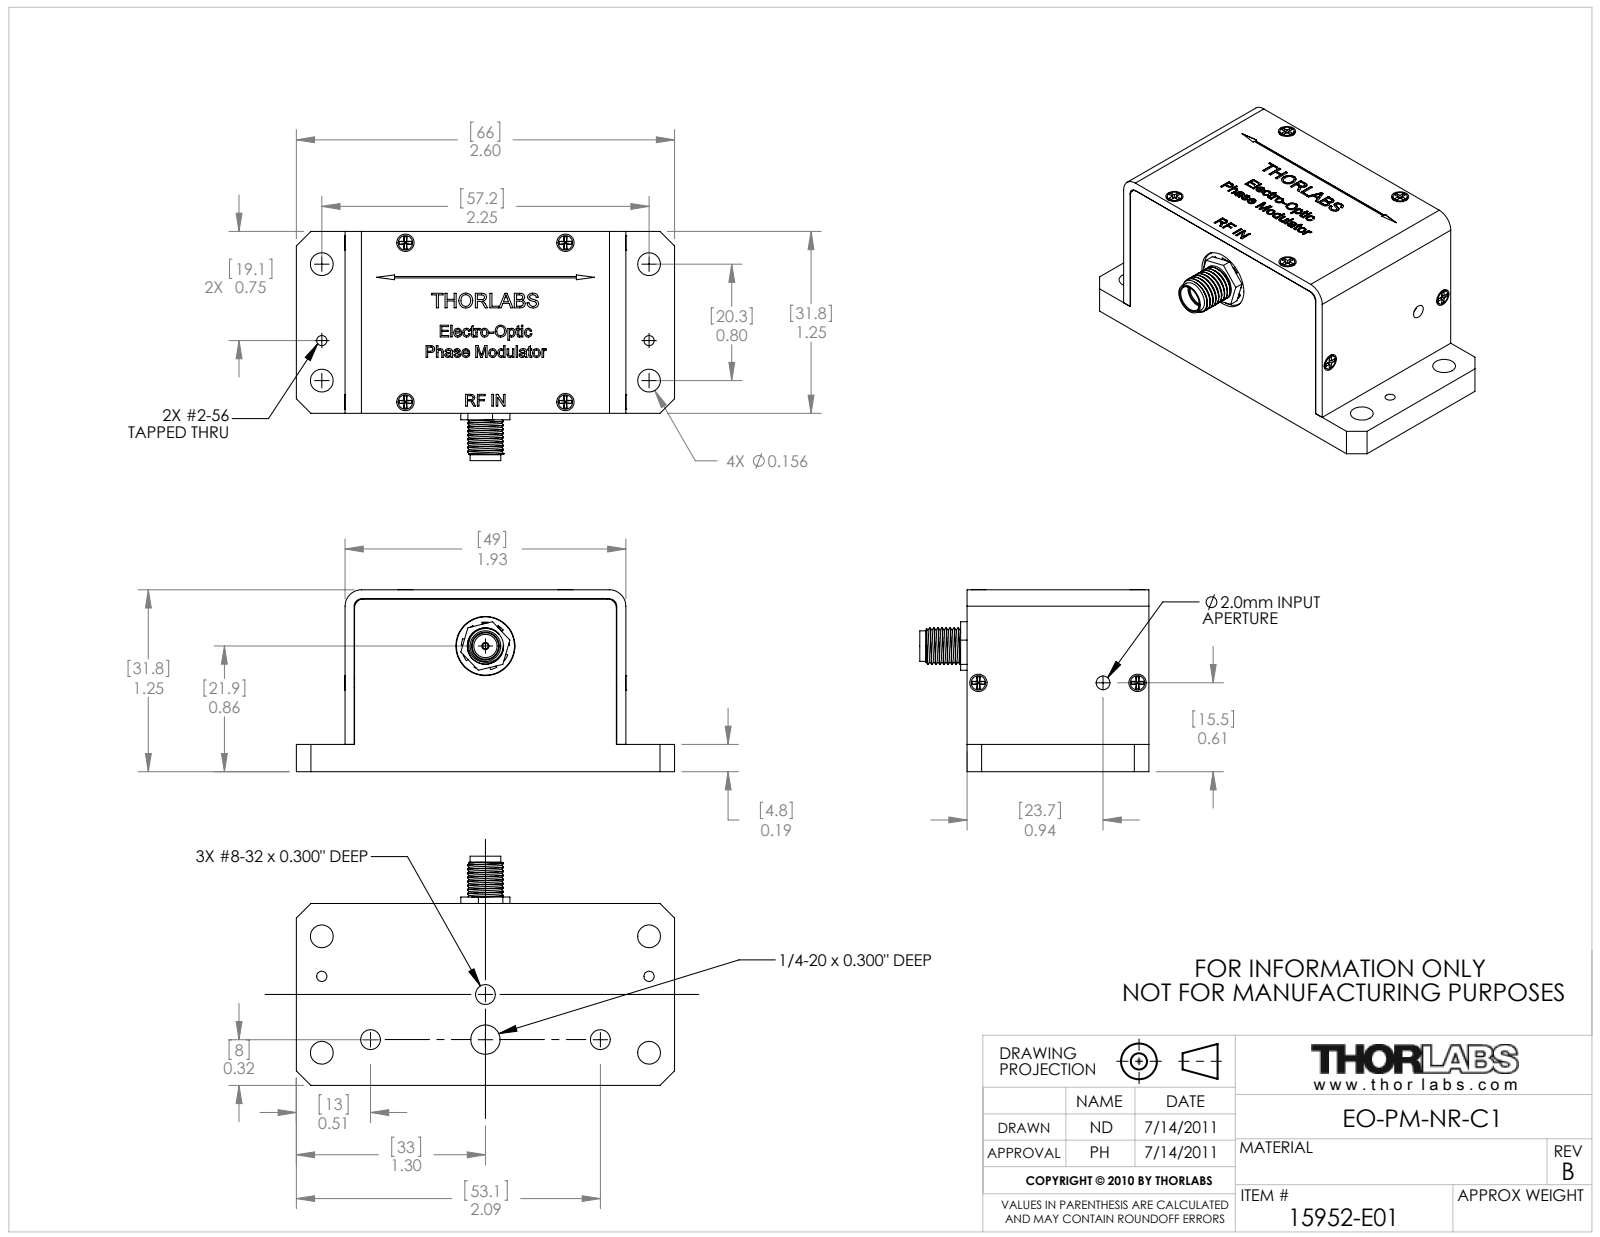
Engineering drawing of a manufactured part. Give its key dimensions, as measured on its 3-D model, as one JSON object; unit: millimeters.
{"part_name": "15952-E01", "step_written_by": "SolidWorks 2011 (AUTOMOTIVE_DESIGN)", "units": "millimeters", "bodies": {"solids": 13, "faces": 997, "planar": 529, "cylindrical": 171, "other": 297}, "overall_size": [66.04, 40.01, 31.79], "volume_mm3": 28528, "surface_area_mm2": 18673, "round_holes": [[1.78, 8], [1.19, 6], [3.97, 4], [3.45, 3], [0.94, 1], [1.27, 1], [2.38, 1], [4.06, 1], [4.19, 1], [4.6, 1], [5.11, 1], [6.35, 1]], "round_bosses_or_shafts": [[2.51, 6], [1.52, 6], [10.16, 1], [8, 1], [6.3, 1], [5.33, 1], [1.27, 1]], "partial_cylinders_radius": [[1.27, 2], [1.59, 2], [2.86, 2], [3.17, 2], [3.26, 2], [3.49, 1], [4.19, 1]], "face_to_face_distances": [31.76, 3.18, 28.58, 30.18, 1.59, 47.43, 25.4, 1.58, 8.89, 21.29], "hole_center_spacings": [15.08, 19.7, 28.14, 30.33, 42.71, 48.88, 27.78, 57.16]}
